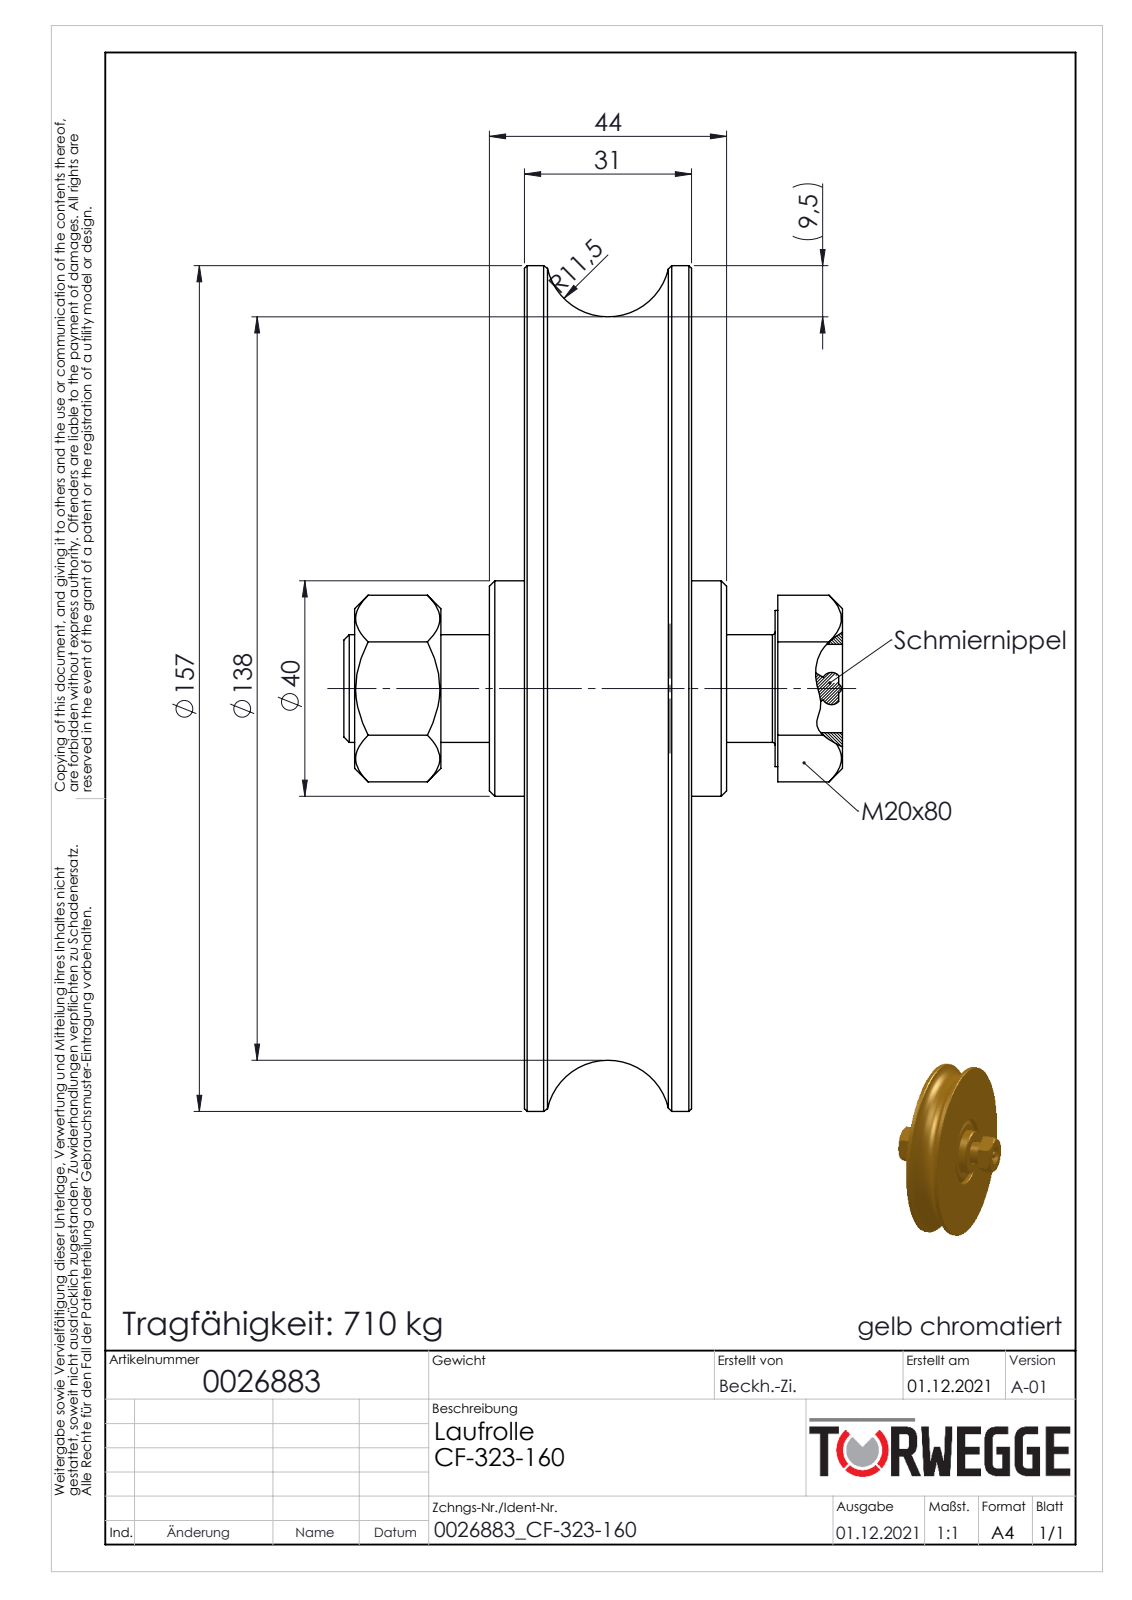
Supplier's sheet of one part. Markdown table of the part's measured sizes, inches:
| quantity | value |
| --- | --- |
| part name | 0026883 |
| STEP written by | SolidWorks 2020 (AUTOMOTIVE_DESIGN) |
| units | inches |
| bodies | 5 solids, 200 faces (76 planar, 44 cylindrical, 80 other) |
| overall size | 6.181 × 6.181 × 3.642 |
| volume | 33.38 in³ |
| surface area | 131.2 in² |
| round holes (diameter × count) | 0.157 × 1, 0.646 × 1, 0.681 × 1, 0.791 × 1, 1.181 × 1, 1.626 × 1, 1.902 × 1, 2.362 × 1, 2.795 × 1, 3.031 × 1 |
| round bosses / shafts (diameter × count) | 6.181 × 1, 1.575 × 1, 1.173 × 1, 1.142 × 1, 0.787 × 1 |
| main face-to-face distances | 1.22, 0.984, 0.236, 1.063, 1.476, 1.24, 1.181, 0.492, 0.748, 0.059 |
